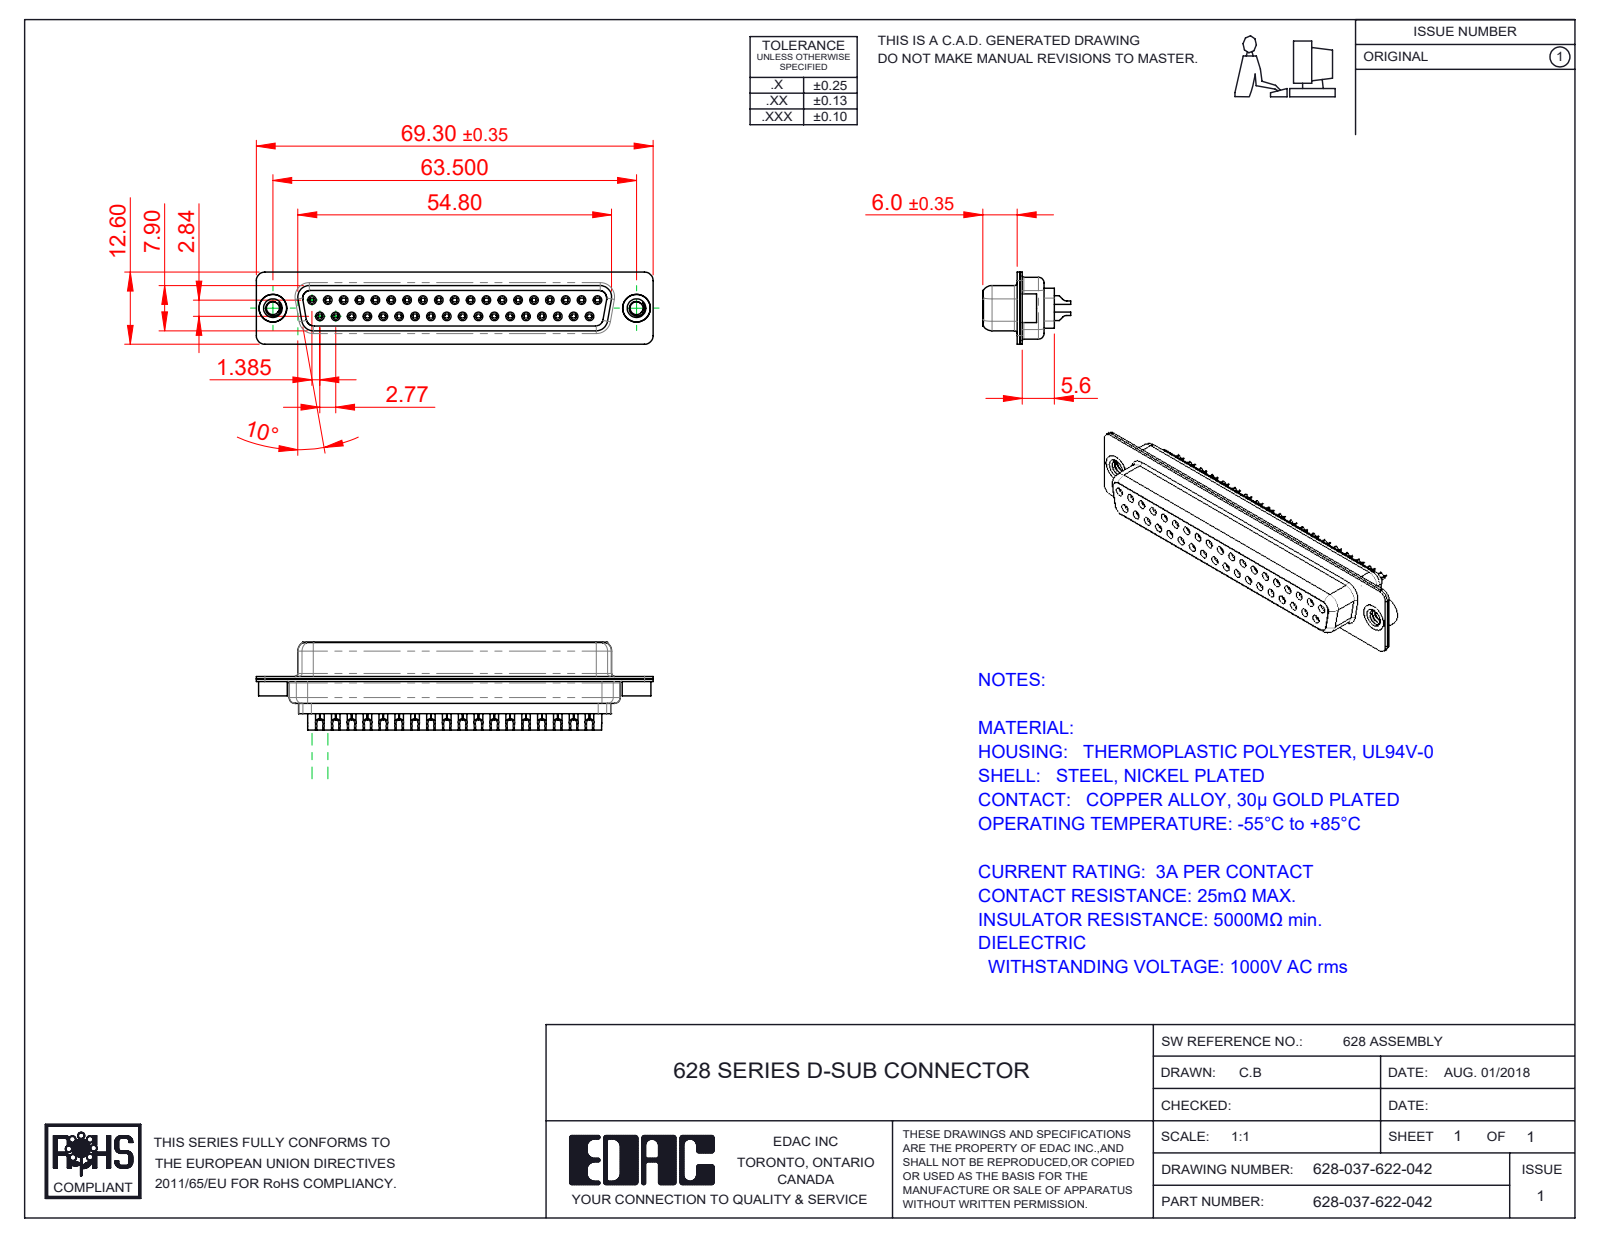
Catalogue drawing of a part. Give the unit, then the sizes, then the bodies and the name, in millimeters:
Units: millimetres
Overall size (bounding box): 69.3 × 15.35 × 12.6
Round holes (diameter × count): ⌀0.8 ×37, ⌀0.9 ×37, ⌀1.1 ×37, ⌀1.6 ×37, ⌀1.7 ×19, ⌀2.26 ×2, ⌀4 ×2, ⌀4.05 ×2, ⌀4.85 ×2
Round bosses / shafts (diameter × count): ⌀2 ×37, ⌀1.5 ×37, ⌀1.2 ×37, ⌀5 ×2, ⌀4.95 ×2, ⌀4.8 ×2
Partial cylindrical surfaces — rounded edges, fillets, slot ends (radius × count): R0.28 ×37, R1.5 ×16, R2 ×12, R1 ×6, R0.25 ×4, R0.5 ×4, R0.6 ×4, R0.65 ×4
Main face-to-face distances: 0.45, 0.4, 6.6, 1.9, 8.5, 1.4, 7.05, 0.85, 7.45, 0.9
Hole centre spacings: 3.16, 2.77, 5.54, 8.31, 5.04, 7.49, 11.08, 13.85
Volume: 5 387 mm³ · Surface area: 13 004 mm²
Bodies: 42 solids, 3568 faces (844 planar, 1060 cylindrical, 1664 other)
Part name (STEP PRODUCT): 628-037-622-042; 628 Contact Row 1_22L; 628 Shell Rear_37 Contacts; 628 4-40 Threaded Rivet (+3 more)
STEP written by: SolidWorks 2020 (CONFIG_CONTROL_DESIGN)
